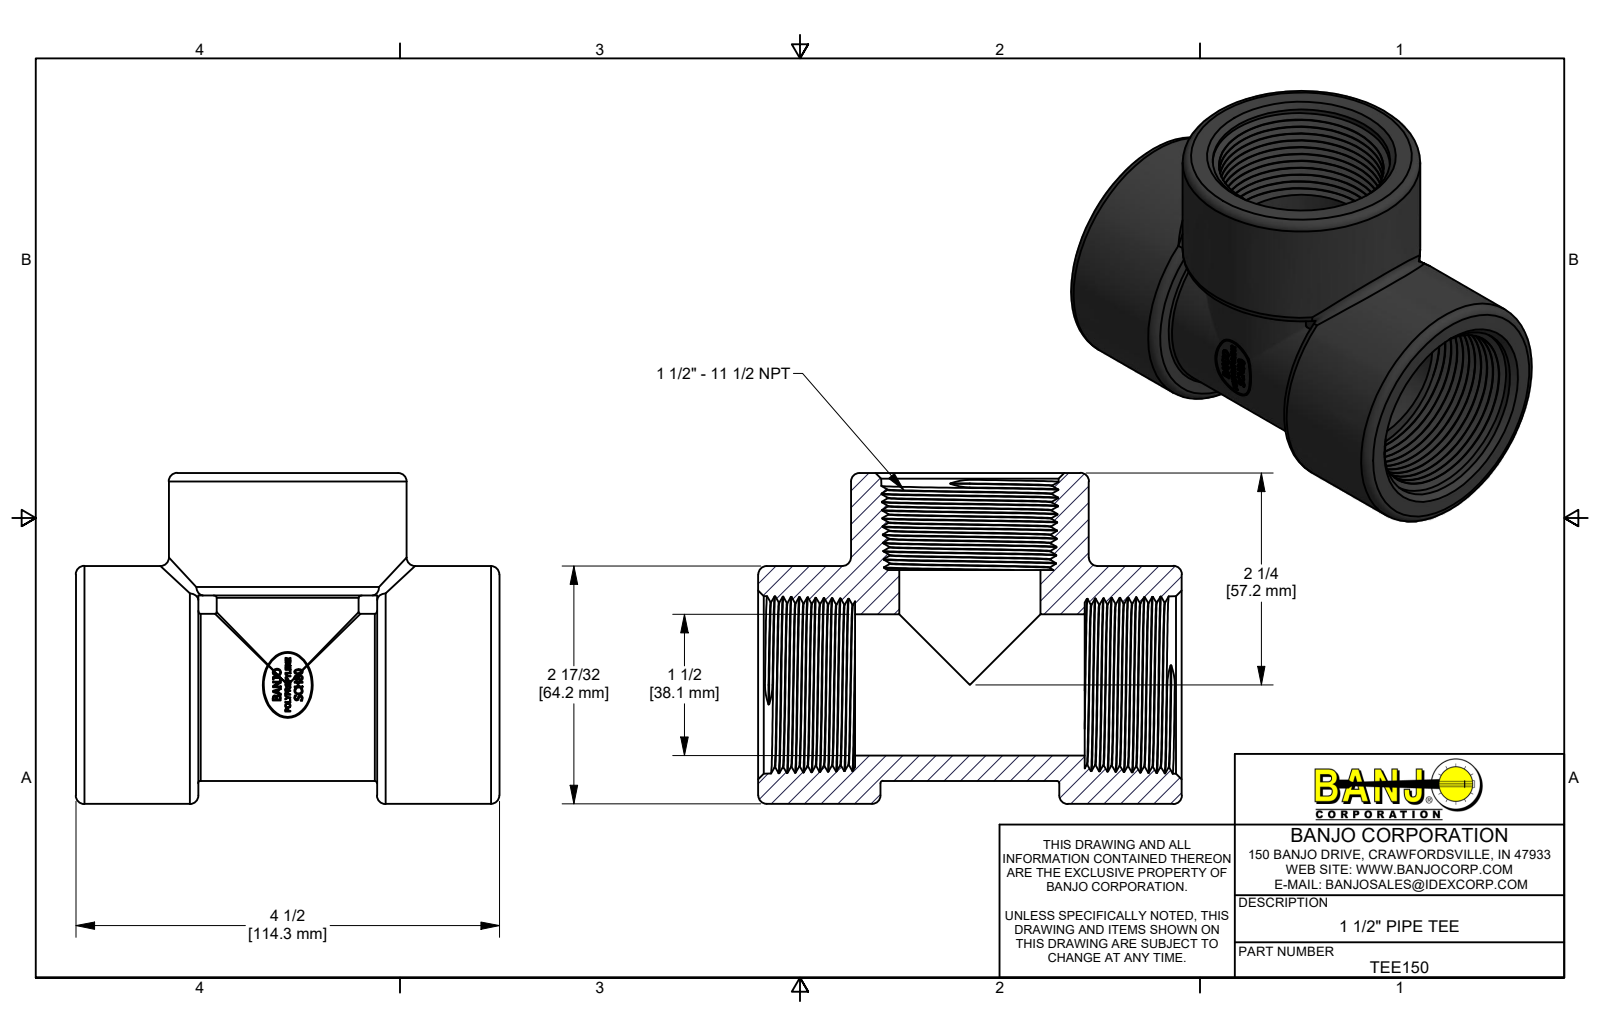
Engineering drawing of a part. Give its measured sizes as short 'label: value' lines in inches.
name: TEE150; TITLBLKB; TITLBLKC; STITBLKC
written by: Mechanical Desktop 2009 (AUTOMOTIVE_DESIGN)
unit: in
bodies: 1 solid, 179 faces (10 planar, 14 cylindrical, 155 other)
size: 4.5 × 3.513 × 2.526
volume: 12.49 in³; area: 95.35 in²
holes: 2× ⌀1.5
bosses: 2× ⌀2.526, 1× ⌀2.04
rounds: 1× R1.02
face distances: 1.3, 3.2, 4.5, 0.956, 0.344, 1.9, 3.543, 2.243, 0.343, 0.957
